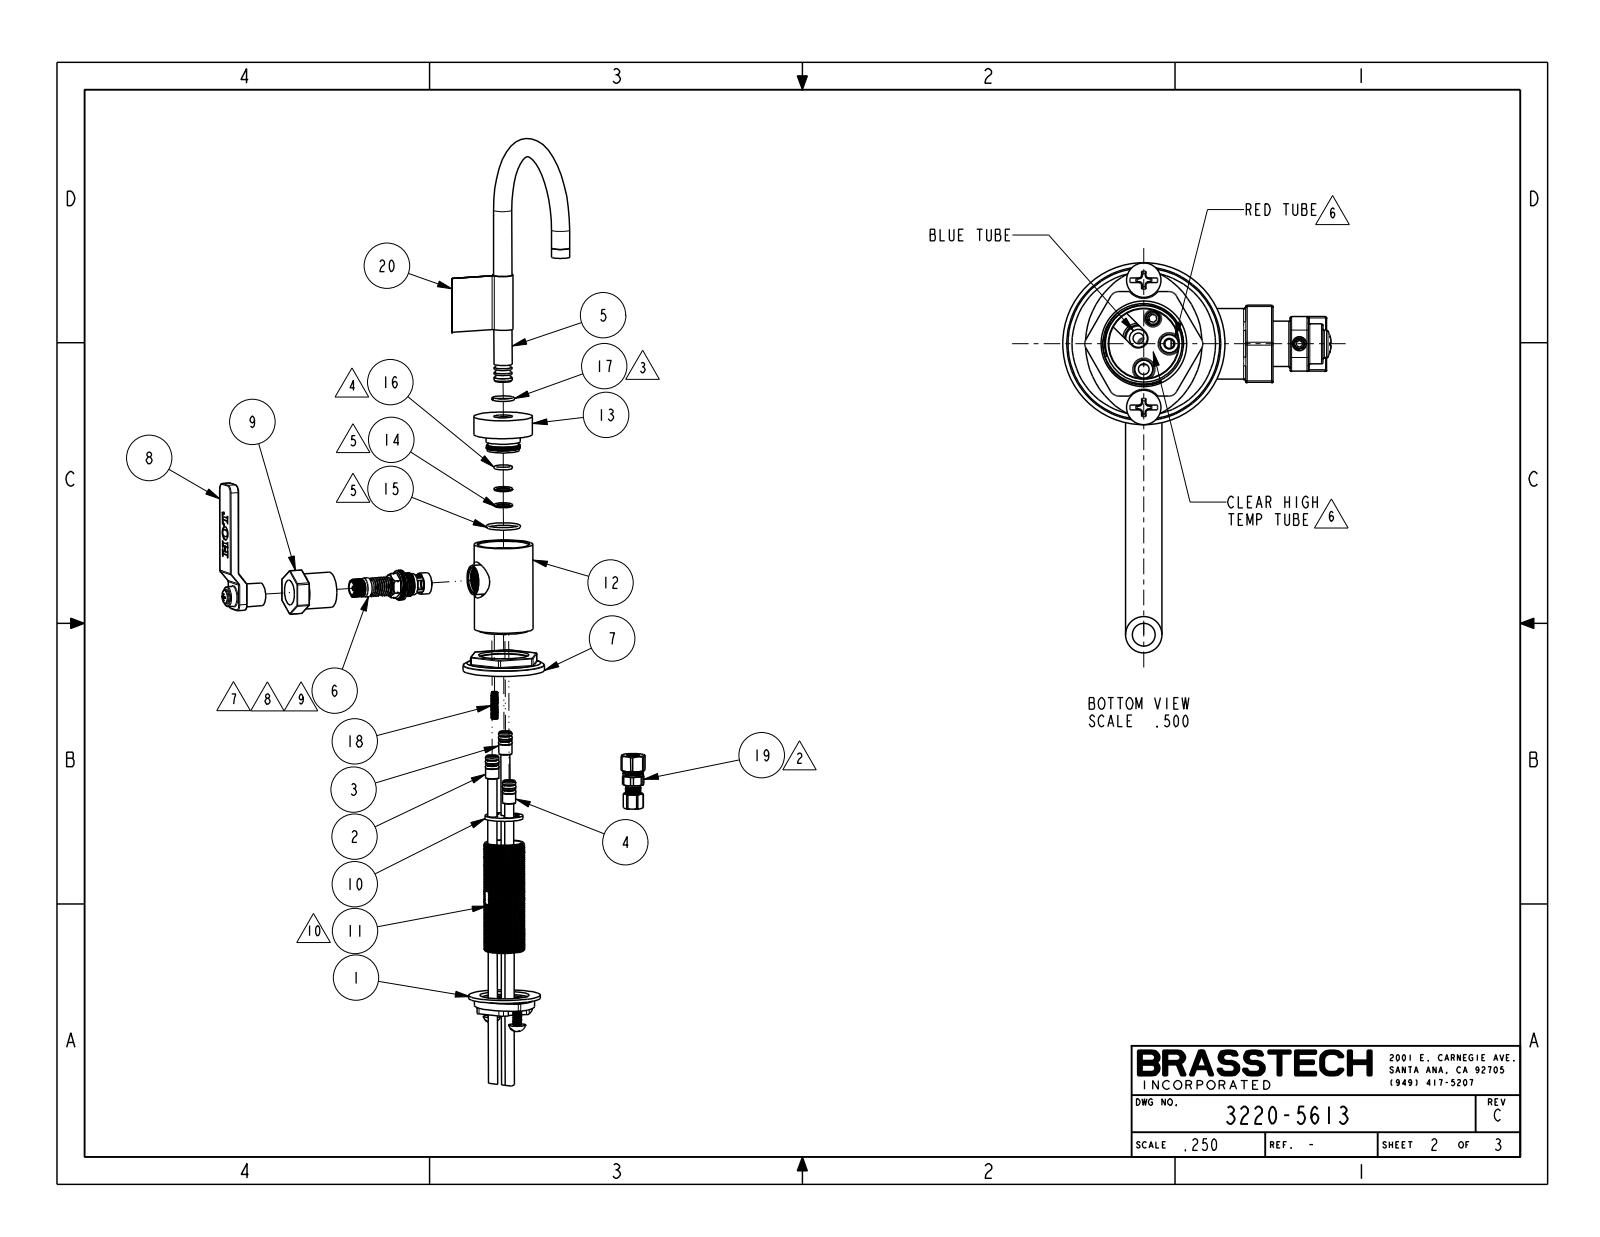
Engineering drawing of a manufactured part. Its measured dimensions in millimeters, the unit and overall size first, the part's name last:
Units: millimetres
Overall size (bounding box): 235.6 × 136.3 × 93.6
Round holes (diameter × count): ⌀25.4 ×1
Round bosses / shafts (diameter × count): ⌀12.7 ×2, ⌀56.6 ×1, ⌀40.9 ×1, ⌀24.6 ×1, ⌀15.9 ×1, ⌀14 ×1, ⌀9.5 ×1
Partial cylindrical surfaces — rounded edges, fillets, slot ends (radius × count): R0.5 ×40, R0.3 ×20, R1.5 ×10, R1 ×6, R4.7 ×4
Main face-to-face distances: 83.2, 6.4, 19.1, 18.7, 12.3, 5.3, 77.9, 43.8, 10.8, 5.5
Volume: 177 300 mm³ · Surface area: 34 450 mm²
Bodies: 1 solid, 394 faces (113 planar, 102 cylindrical, 179 other)
Part name (STEP PRODUCT): 3220-5613
STEP written by: CREO PARAMETRIC BY PTC INC, 2018400 (CONFIG_CONTROL_DESIGN)
